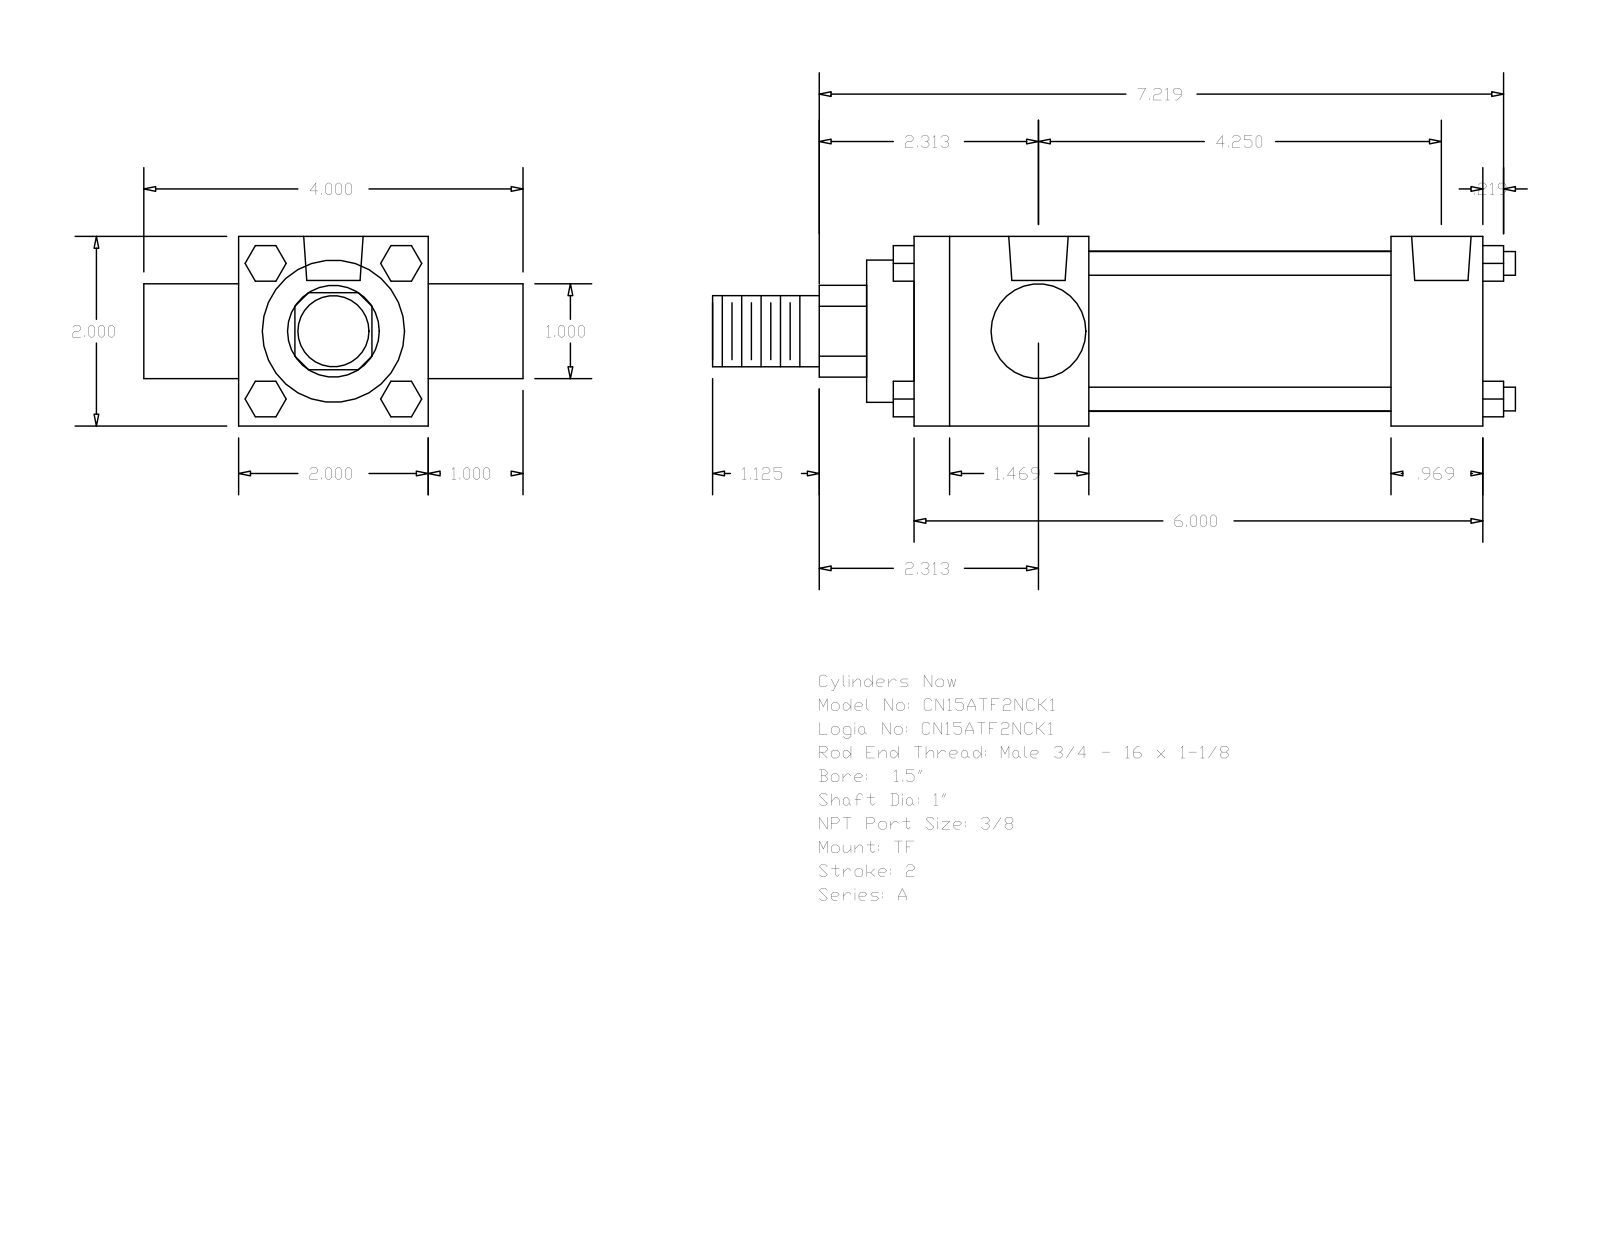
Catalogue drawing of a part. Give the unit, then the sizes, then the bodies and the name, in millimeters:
Units: millimetres
Overall size (bounding box): 215.11 × 101.6 × 50.8
Round holes (diameter × count): ⌀5.56 ×3, ⌀15.93 ×2
Round bosses / shafts (diameter × count): ⌀6.35 ×4, ⌀25.4 ×2, ⌀42.93 ×1, ⌀38.1 ×1, ⌀19.05 ×1
Partial cylindrical surfaces — rounded edges, fillets, slot ends (radius × count): R12.29 ×1
Main face-to-face distances: 50.8, 25.4, 152.4, 76.2, 46.83, 127.79, 80.96, 105.57, 24.61, 12.7
Hole centre spacings: 3.97, 103.98, 100.01, 107.95
Bodies: 0 solids, 120 faces (92 planar, 28 cylindrical, 0 other)
Part name (STEP PRODUCT): A_TF__0150_1
STEP written by: GSSL Pune (CONFIG_CONTROL_DESIGN)
